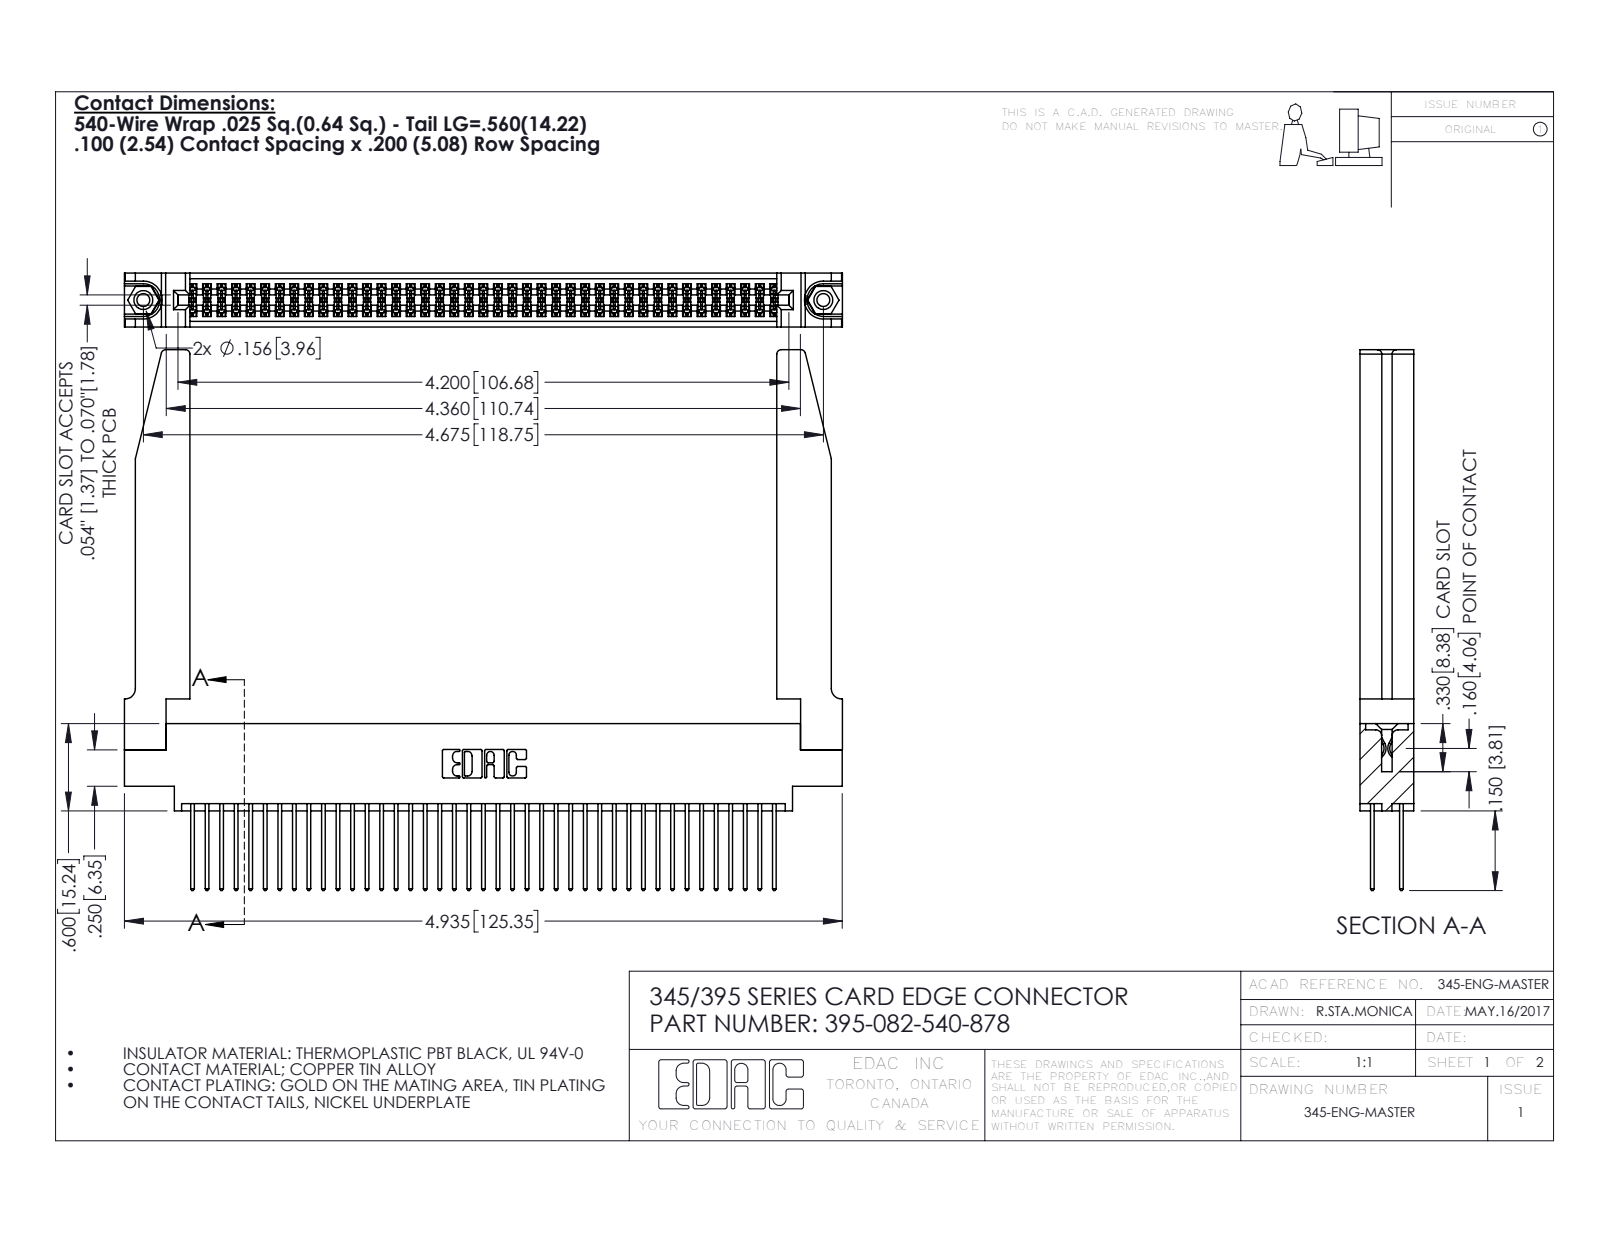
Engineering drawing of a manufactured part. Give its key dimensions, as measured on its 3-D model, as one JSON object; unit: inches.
{"part_name": "345-292-001_345-293-140; 345 Part_0.170 Offset - 0.156 Dia-TH; 345-250-001_345-250-001-102; 395-082-540-878 (+1 more)", "step_written_by": "SolidWorks 2016 (CONFIG_CONTROL_DESIGN)", "units": "inches", "bodies": {"solids": 87, "faces": 4464, "planar": 2932, "cylindrical": 1480, "other": 52}, "overall_size": [4.936, 3.717, 0.37], "volume_in3": 1.229, "surface_area_in2": 41.36, "round_holes": [[0.089, 2], [0.125, 2], [0.156, 2], [0.064, 1]], "round_bosses_or_shafts": [[0.155, 2]], "partial_cylinders_radius": [[0.006, 123], [0.01, 82], [0.01, 22], [0.03, 8], [0.007, 6], [0.031, 6], [0.026, 3], [0.014, 2]], "face_to_face_distances": [0.072, 0.298, 0.37, 0.2, 0.098, 0.272, 0.025, 0.225, 0.175, 0.148], "hole_center_spacings": [0.27, 4.439, 4.675]}
